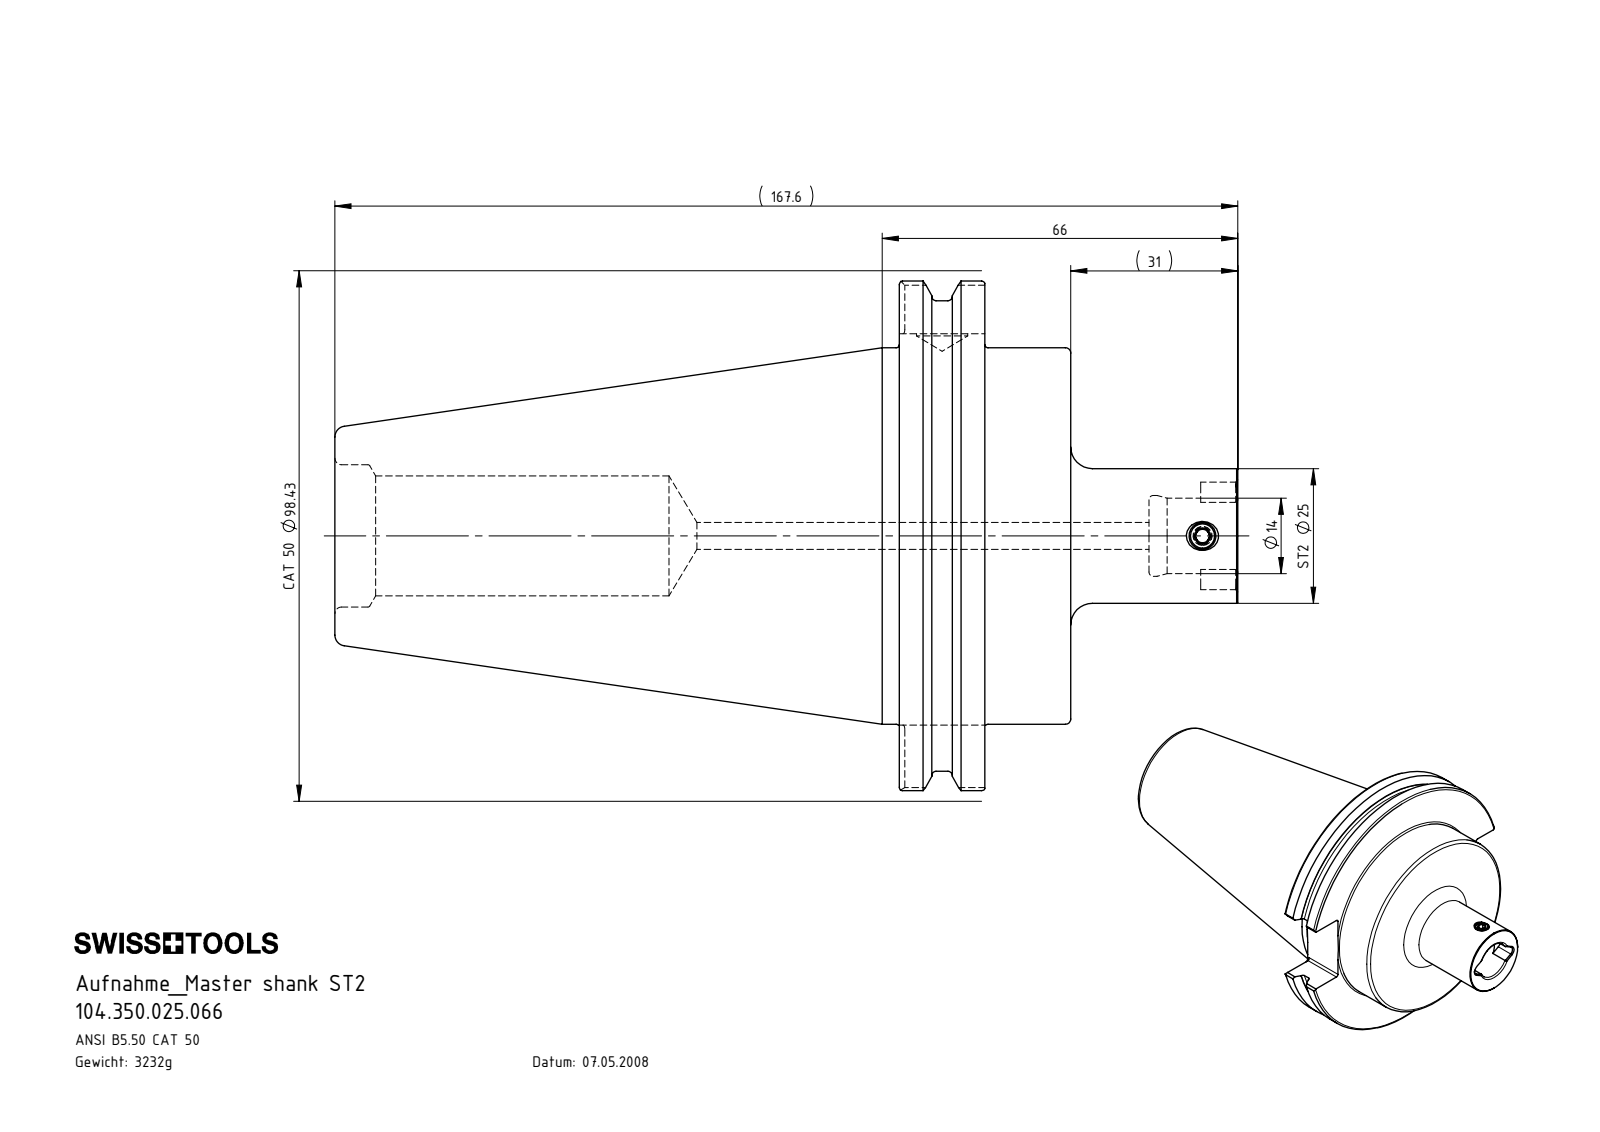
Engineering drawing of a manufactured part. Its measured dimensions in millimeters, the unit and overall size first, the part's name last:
Units: millimetres
Overall size (bounding box): 167.6 × 98.42 × 94.52
Round holes (diameter × count): ⌀2.5 ×1, ⌀4.5 ×1, ⌀5 ×1, ⌀9.5 ×1, ⌀14 ×1, ⌀15 ×1, ⌀22.25 ×1, ⌀26.4 ×1
Round bosses / shafts (diameter × count): ⌀98.42 ×1, ⌀91 ×1, ⌀69.85 ×1, ⌀25 ×1, ⌀5 ×1
Partial cylindrical surfaces — rounded edges, fillets, slot ends (radius × count): R0.8 ×8, R1.8 ×2
Main face-to-face distances: 15.87, 31.82, 15.95, 104.78, 120.65, 136.6, 72.6, 167.6, 62.82, 46.95
Volume: 411 716 mm³ · Surface area: 48 287 mm²
Bodies: 2 solids, 115 faces (50 planar, 28 cylindrical, 37 other)
Part name (STEP PRODUCT): CT5.ST2.K01.066; CT5-ST2.K01.066_B; ST2-ER1.001.006_A
STEP written by: SolidWorks 2017 (AUTOMOTIVE_DESIGN)
